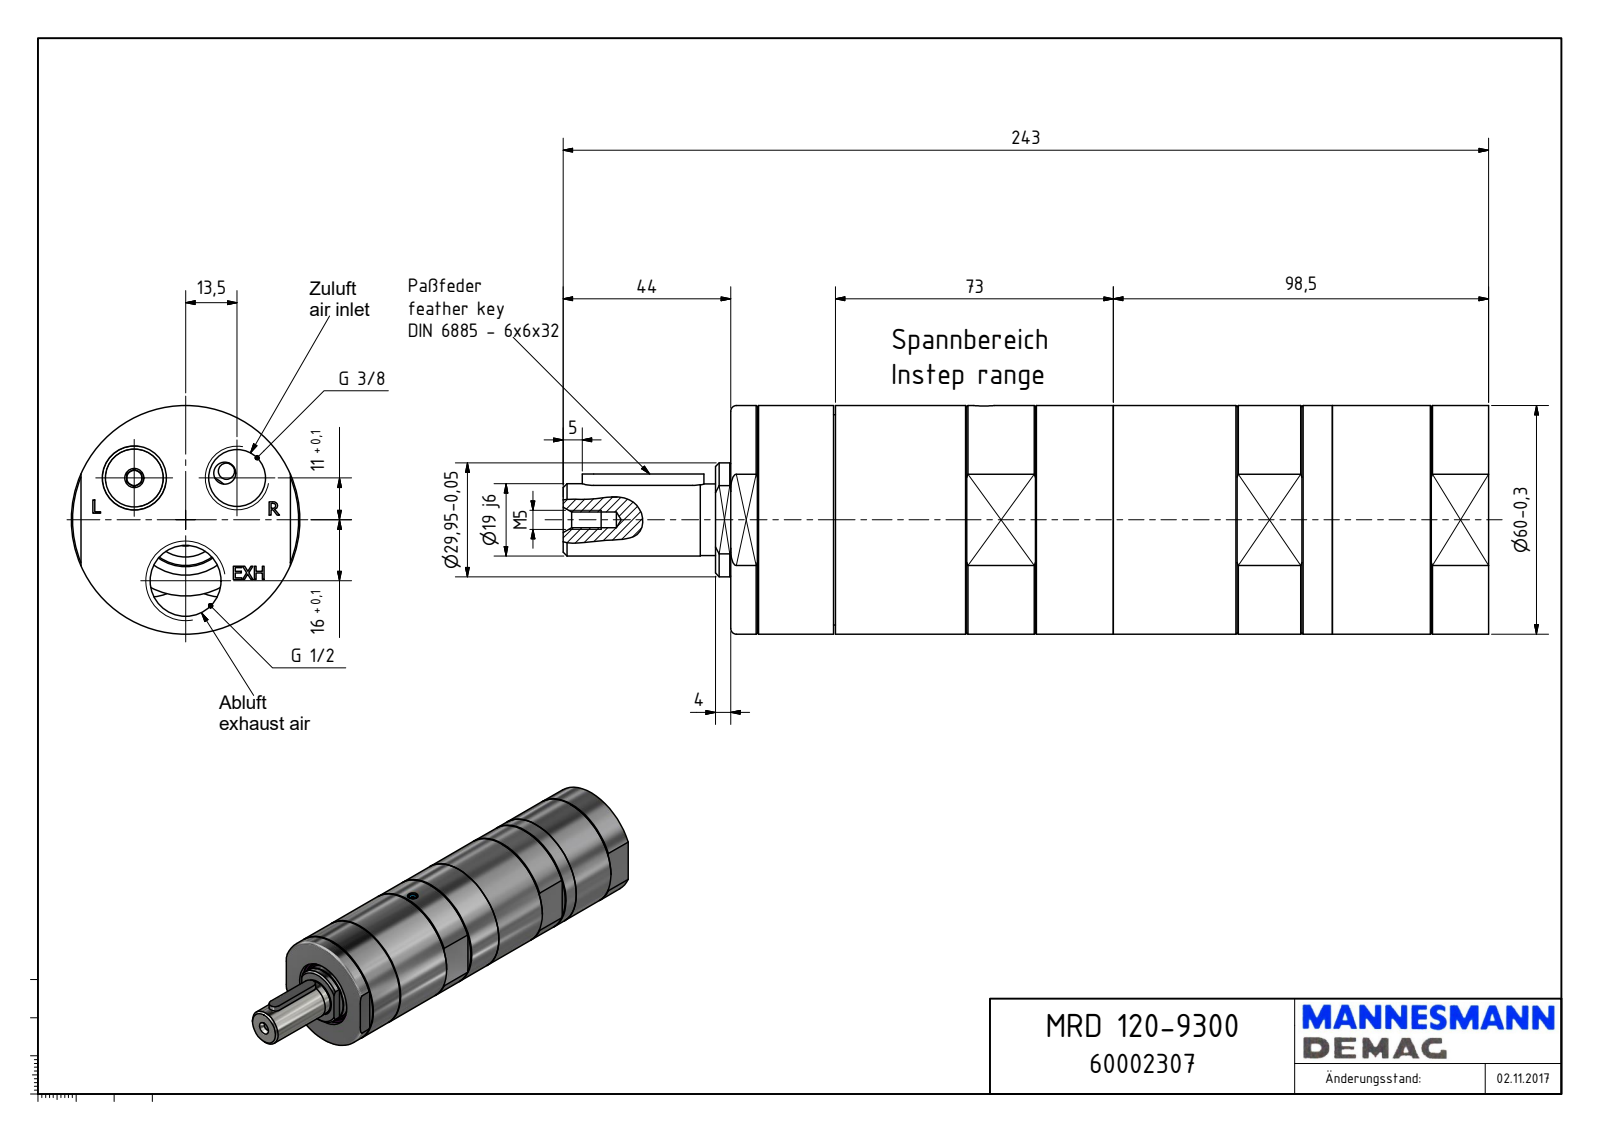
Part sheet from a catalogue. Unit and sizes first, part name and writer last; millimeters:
Units: millimetres
Overall size (bounding box): 243 × 60 × 60
Round holes (diameter × count): ⌀4 ×2, ⌀14.95 ×2, ⌀1.55 ×1, ⌀4.13 ×1, ⌀5.5 ×1, ⌀18.63 ×1, ⌀35 ×1, ⌀55.38 ×1
Round bosses / shafts (diameter × count): ⌀60 ×1, ⌀55.18 ×1, ⌀29.95 ×1, ⌀19 ×1, ⌀18.8 ×1, ⌀5 ×1, ⌀3.6 ×1
Partial cylindrical surfaces — rounded edges, fillets, slot ends (radius × count): R2.9 ×2, R3 ×2, R7.5 ×2, R8.5 ×1, R18.87 ×1, R23.5 ×1, R26.8 ×1
Main face-to-face distances: 199, 55, 182.94, 16.06, 186, 3.06, 13, 158.5, 27.5, 155.44
Hole centre spacings: 17.41, 30.19, 16, 27
Volume: 559 682 mm³ · Surface area: 52 668 mm²
Bodies: 1 solid, 219 faces (124 planar, 47 cylindrical, 48 other)
Part name (STEP PRODUCT): MRD 120-9300_60002307
STEP written by: Autodesk Inventor 2018 (AUTOMOTIVE_DESIGN)
